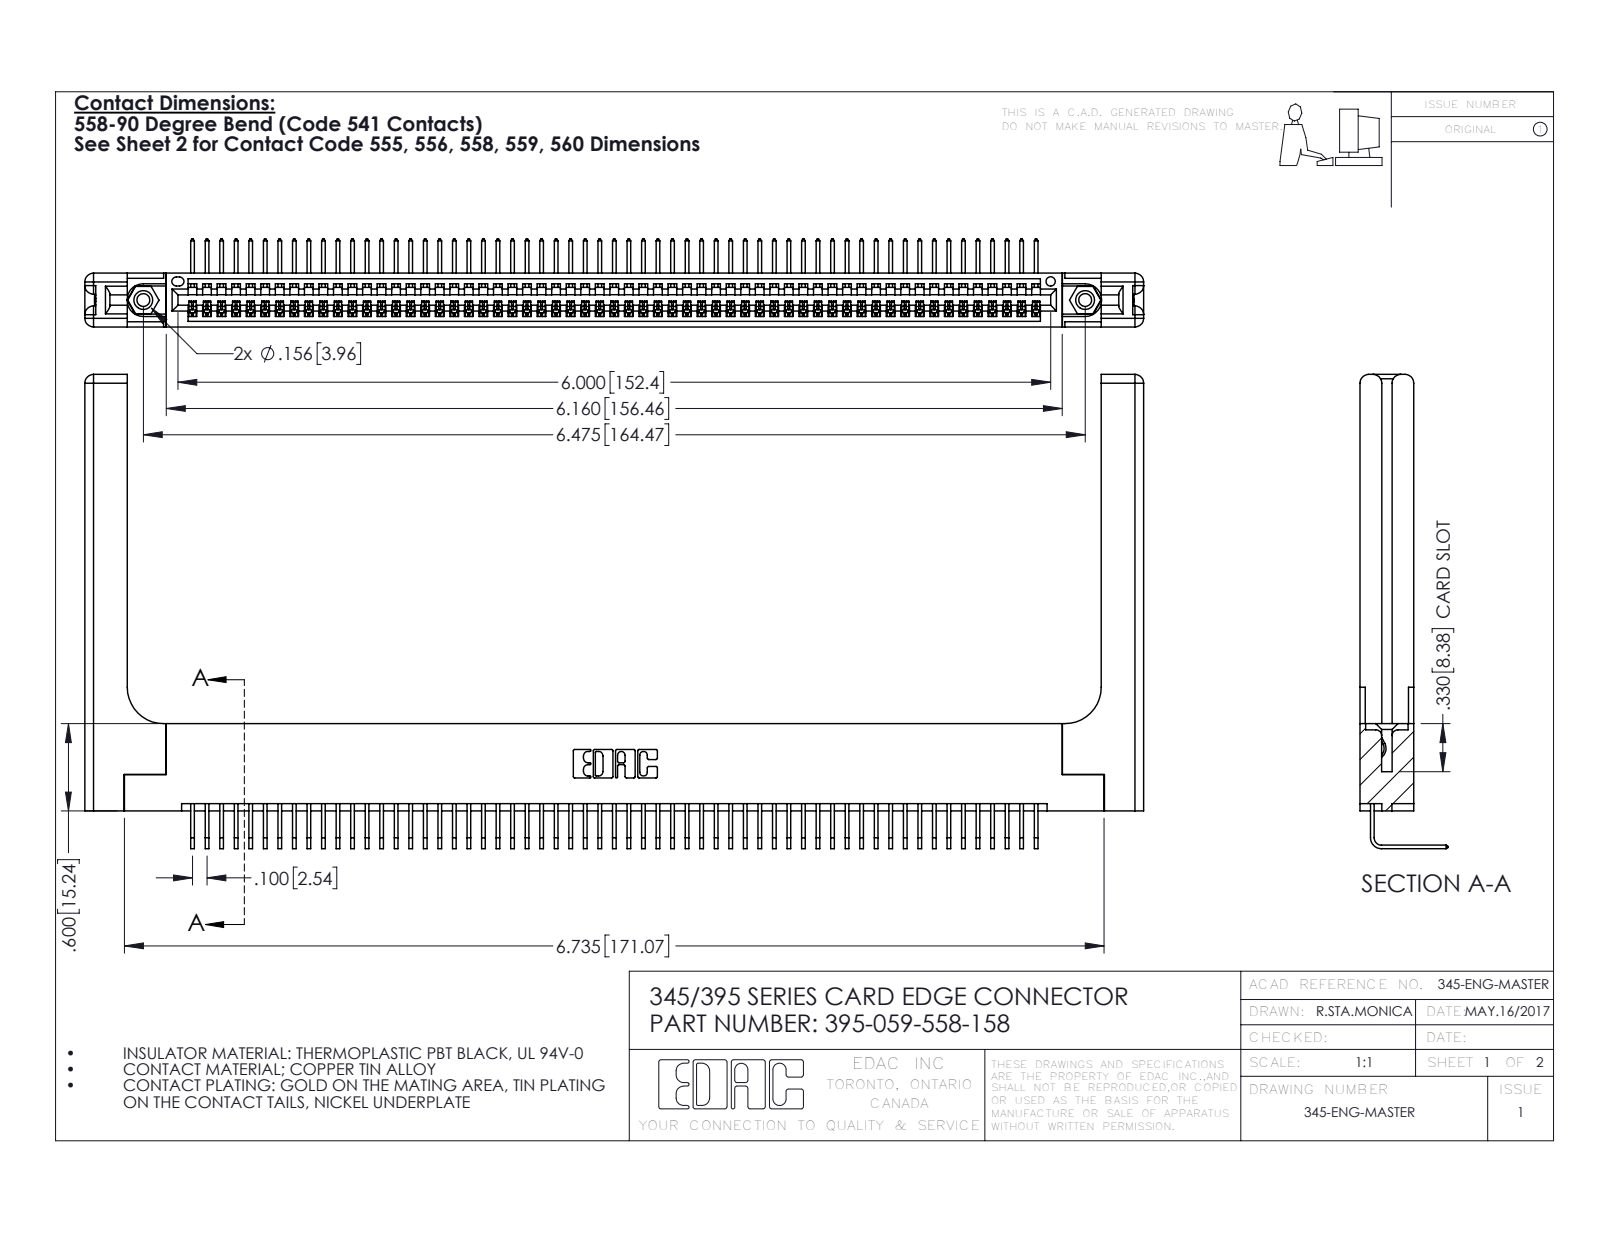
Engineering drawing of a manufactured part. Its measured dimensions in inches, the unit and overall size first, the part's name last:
Units: inches
Overall size (bounding box): 7.279 × 3.259 × 0.605
Round holes (diameter × count): ⌀0.089 ×2, ⌀0.125 ×2, ⌀0.156 ×2, ⌀0.064 ×1
Round bosses / shafts (diameter × count): ⌀0.155 ×2
Partial cylindrical surfaces — rounded edges, fillets, slot ends (radius × count): R0.006 ×118, R0.01 ×22, R0.06 ×16, R0.007 ×6, R0.031 ×6, R0.026 ×3, R0.03 ×2, R0.031 ×2
Main face-to-face distances: 0.072, 0.37, 0.298, 0.2, 0.098, 0.272, 0.025, 0.225, 0.148, 0.15
Hole centre spacings: 0.27, 6.239, 6.475
Volume: 1.611 in³ · Surface area: 47.24 in²
Bodies: 64 solids, 3922 faces (2706 planar, 1156 cylindrical, 60 other)
Part name (STEP PRODUCT): 345-250-001_345-250-001-102; 395-059-558-158; 345-220-058_345-220-058; 345 Part_Flush Mounting Lugs - 0.156 Dia-TH (+1 more)
STEP written by: SolidWorks 2016 (CONFIG_CONTROL_DESIGN)
